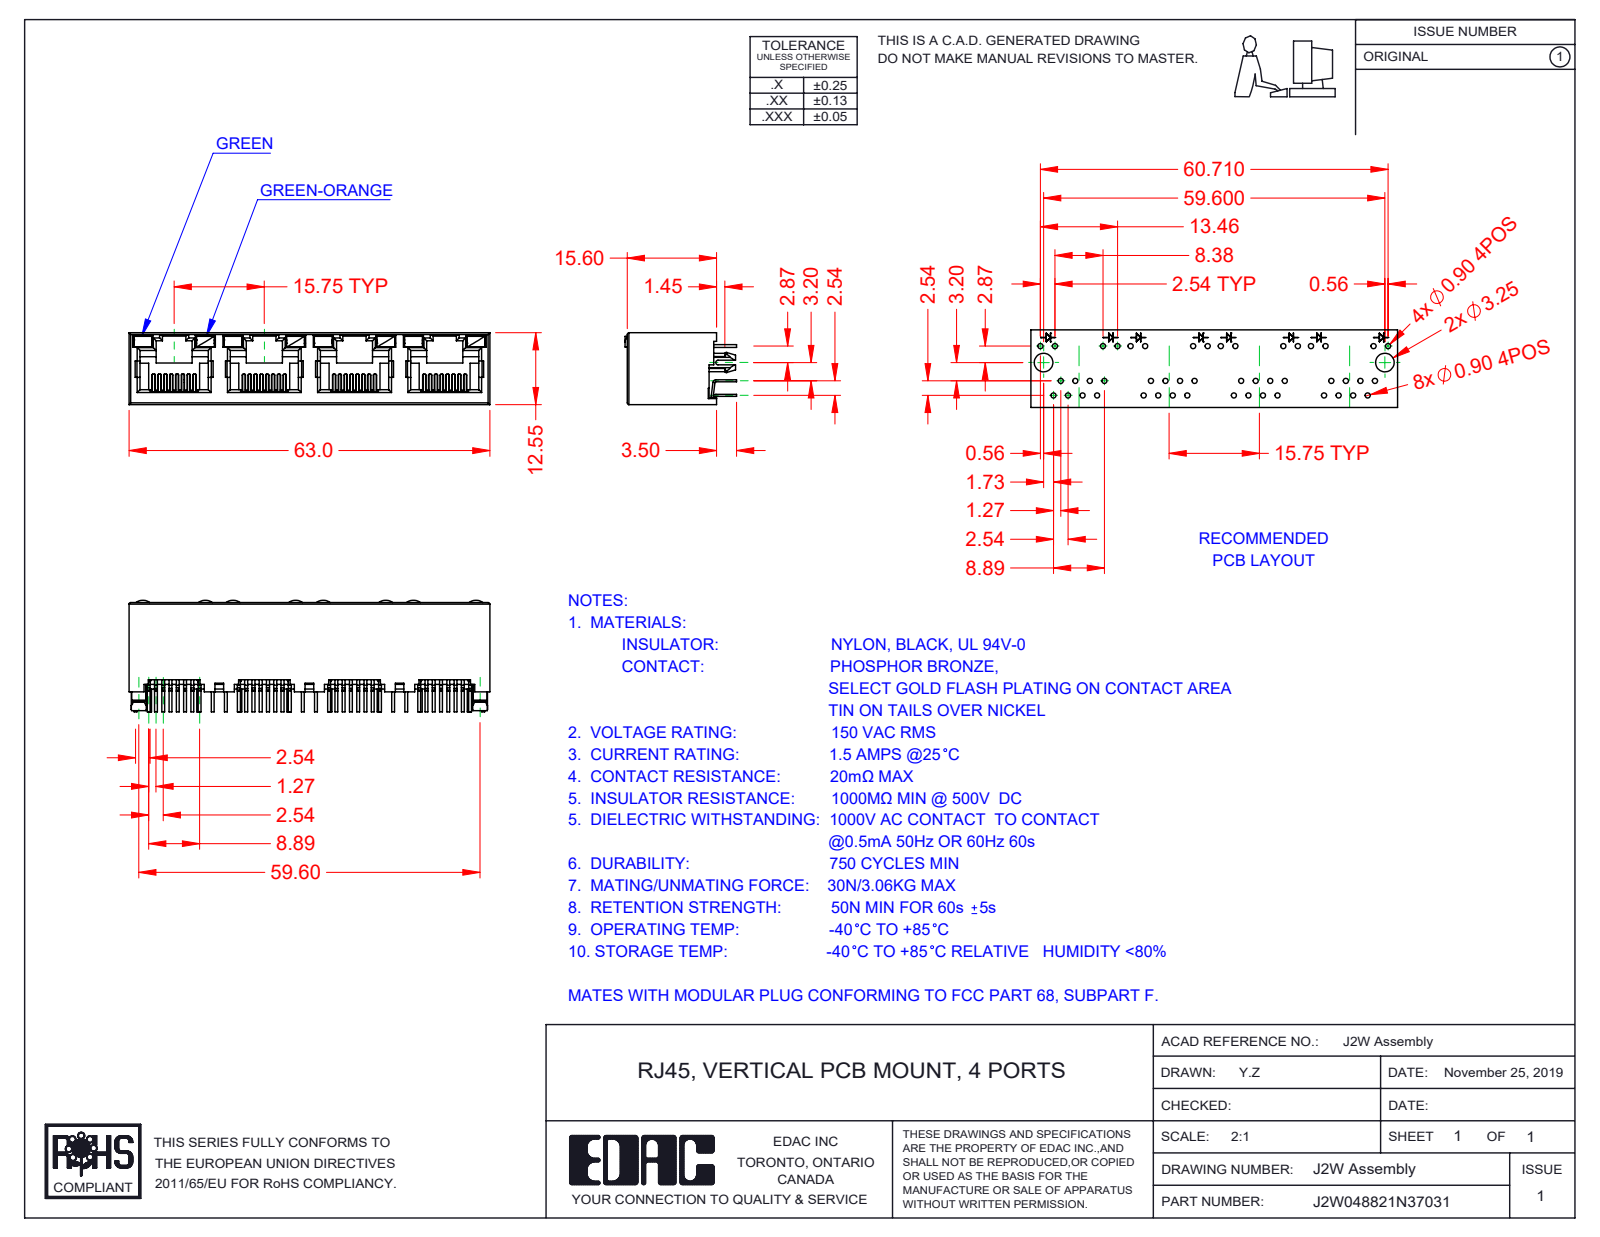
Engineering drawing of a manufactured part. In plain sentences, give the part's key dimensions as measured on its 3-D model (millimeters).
The part is named "2W LED LH_3-Green; 2W Contact Lock; 2W Contacts; J2W048821N37031 (+2 more)". Its 3-D file was written by "SolidWorks 2020 (CONFIG_CONTROL_DESIGN)". It is 45 solids with 3139 faces: 2600 planar, 481 cylindrical and 58 other. Overall it measures 63 by 19.5 by 12.55 millimeters. Its volume is 5 335 cubic millimeters and its surface area 13 144 square millimeters. Partial cylindrical surfaces (rounded edges, fillets, slot ends): 64 of radius 0.15, 29 of radius 0.2, 28 of radius 0.5, 14 of radius 0.3, 8 of radius 0.45, 8 of radius 2, 2 of radius 0.25, 2 of radius 1.5. The main face-to-face distances are 12.55, 11.9, 0.65, 15.75, 0.36, 1.5, 0.78, 0.6, 11.3, 31.5.
